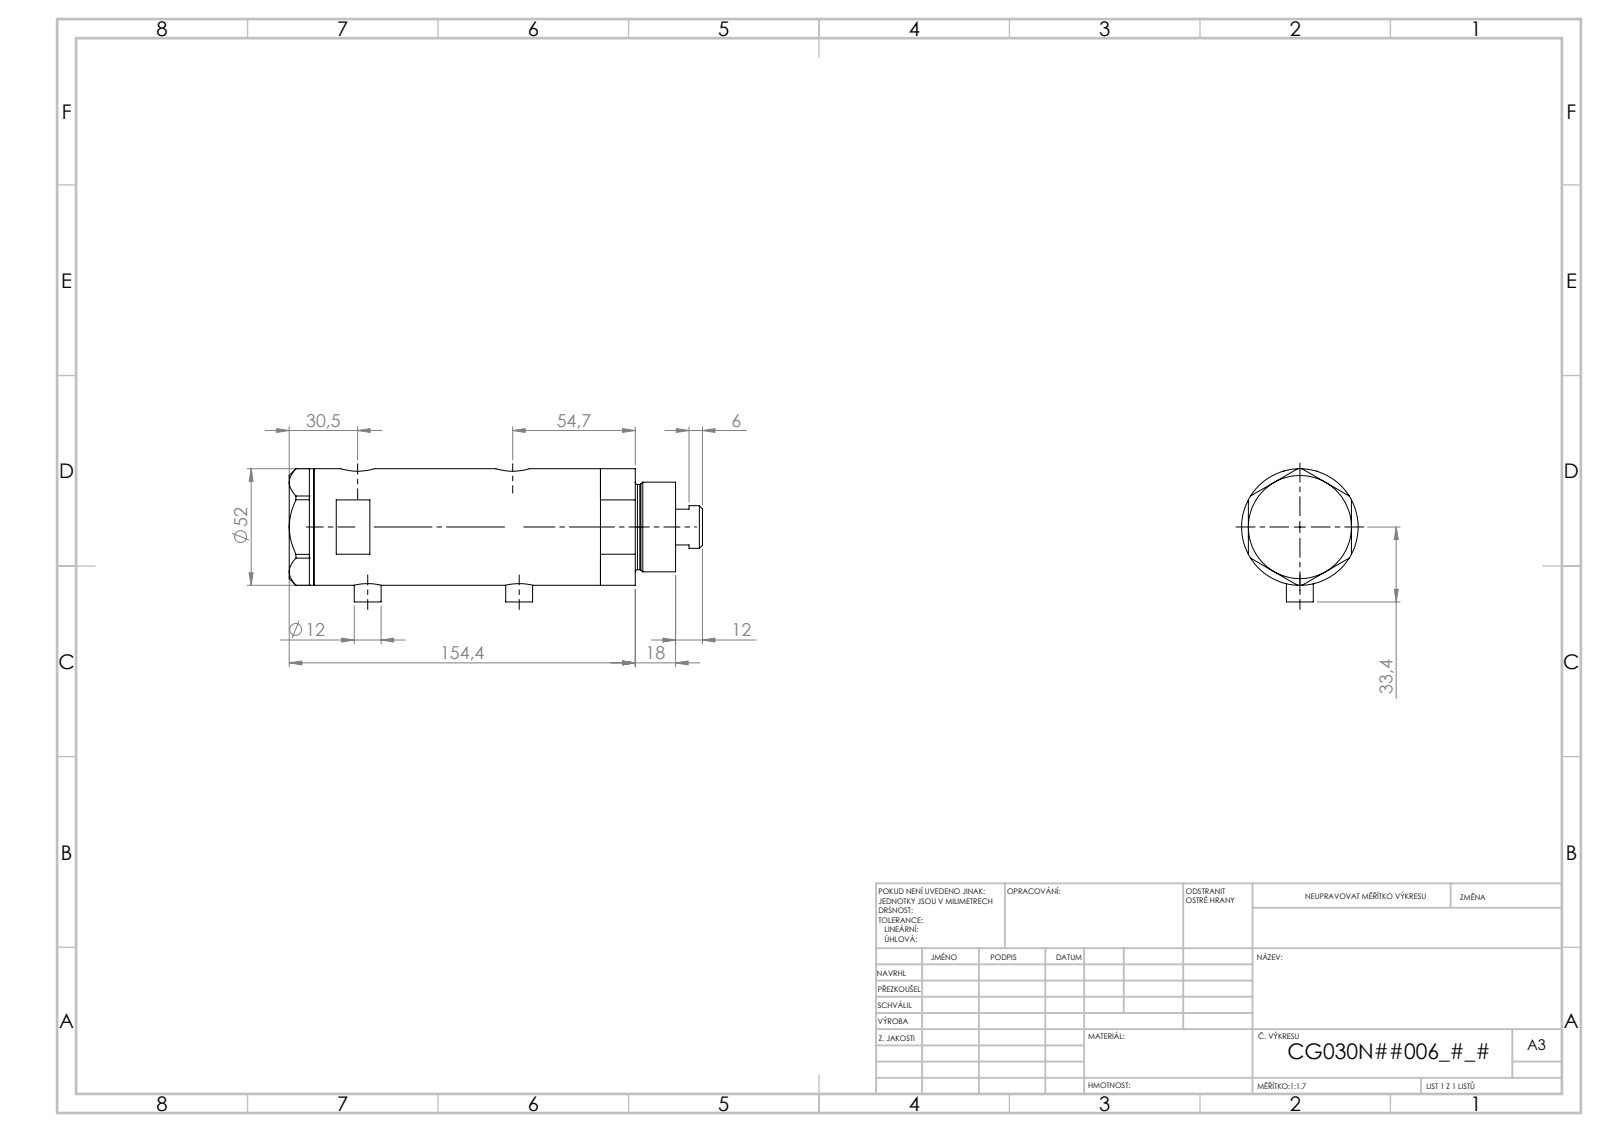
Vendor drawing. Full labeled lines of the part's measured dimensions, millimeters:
Part name (STEP PRODUCT): V270CG_FRONT; V270CG_VC; V270CG_BACK; V270CG_MIDDLE
STEP written by: SolidWorks 2019 (CONFIG_CONTROL_DESIGN)
Units: millimetres
Bodies: 4 solids, 140 faces (67 planar, 53 cylindrical, 20 other)
Overall size (bounding box): 155.02 × 53.1 × 52
Volume: 277 905 mm³ · Surface area: 67 012 mm²
Round holes (diameter × count): ⌀5 ×2, ⌀9.73 ×2, ⌀12.5 ×2, ⌀15 ×2, ⌀6.5 ×1, ⌀20 ×1, ⌀21.5 ×1, ⌀30 ×1, ⌀33 ×1, ⌀44 ×1
Round bosses / shafts (diameter × count): ⌀12 ×2, ⌀52 ×1, ⌀40 ×1, ⌀38 ×1, ⌀19 ×1
Main face-to-face distances: 59.56, 23.8, 35.76, 11, 34.8, 70.56, 46, 106.96, 95.96, 72.16
Hole centre spacings: 2.9, 4.5, 32.75, 35.65, 37.25, 40.15, 2.89, 2.91
